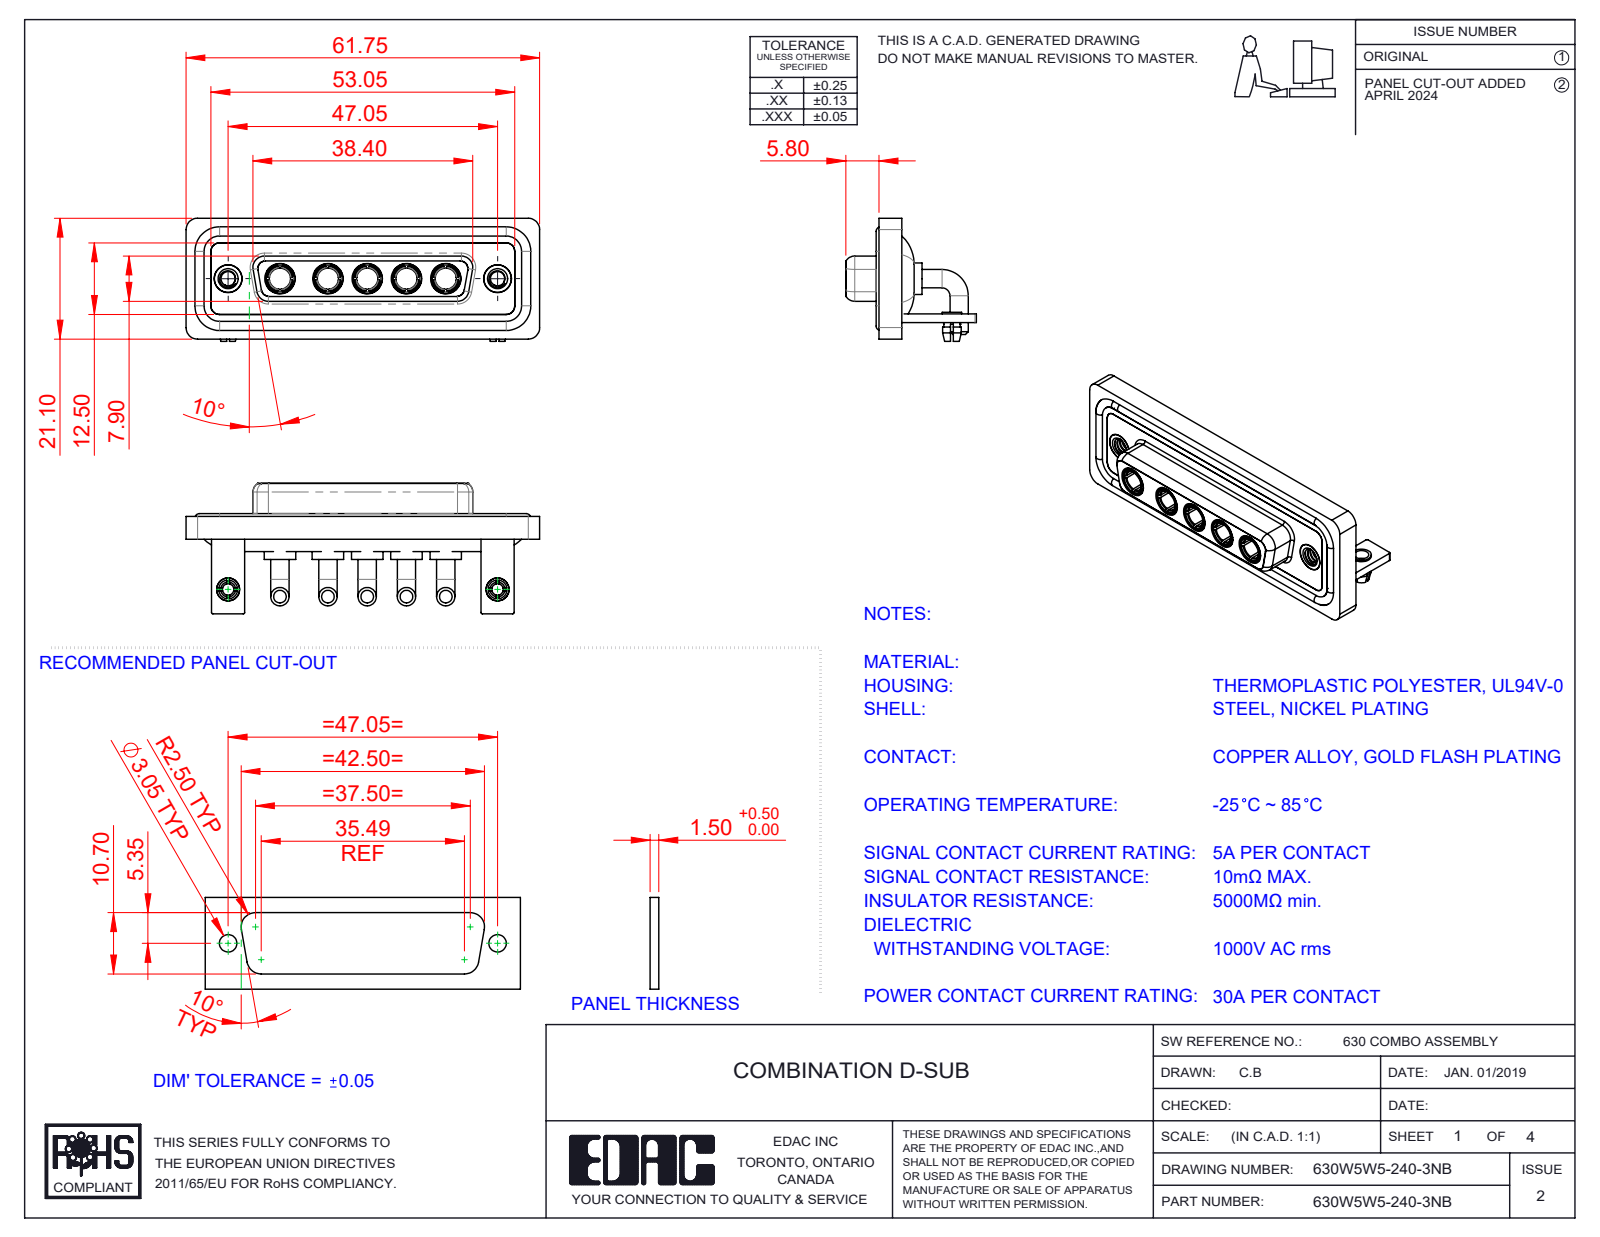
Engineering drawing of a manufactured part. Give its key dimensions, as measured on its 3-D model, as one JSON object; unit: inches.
{"part_name": "630Combo Stabilizer Bracket_50 Contacts; 630Combo Housing_5W5; 630Combo Board Lock_50 Contacts; 630W5W5-240-3NB (+5 more)", "step_written_by": "SolidWorks 2023 (CONFIG_CONTROL_DESIGN)", "units": "inches", "bodies": {"solids": 21, "faces": 910, "planar": 318, "cylindrical": 367, "other": 225}, "overall_size": [2.431, 0.898, 0.846], "volume_in3": 0.547, "surface_area_in2": 23.02, "round_holes": [[0.191, 7], [0.146, 5], [0.209, 5], [0.098, 4], [0.079, 2], [0.126, 2], [0.157, 2], [0.159, 2], [0.197, 2]], "round_bosses_or_shafts": [[0.126, 10], [0.217, 5], [0.205, 5], [0.195, 5], [0.187, 5], [0.148, 5], [0.063, 4], [0.195, 2]], "partial_cylinders_radius": [[0.079, 19], [0.059, 18], [0.01, 16], [0.053, 8], [0.063, 8], [0.02, 5], [0.083, 5], [0.024, 4]], "face_to_face_distances": [0.016, 0.071, 0.114, 0.146, 0.059, 0.161, 0.043, 0.055, 0.063, 0.098], "hole_center_spacings": [0.27, 0.356, 1.496, 1.852, 0.27, 0.33, 0.54, 0.541]}
